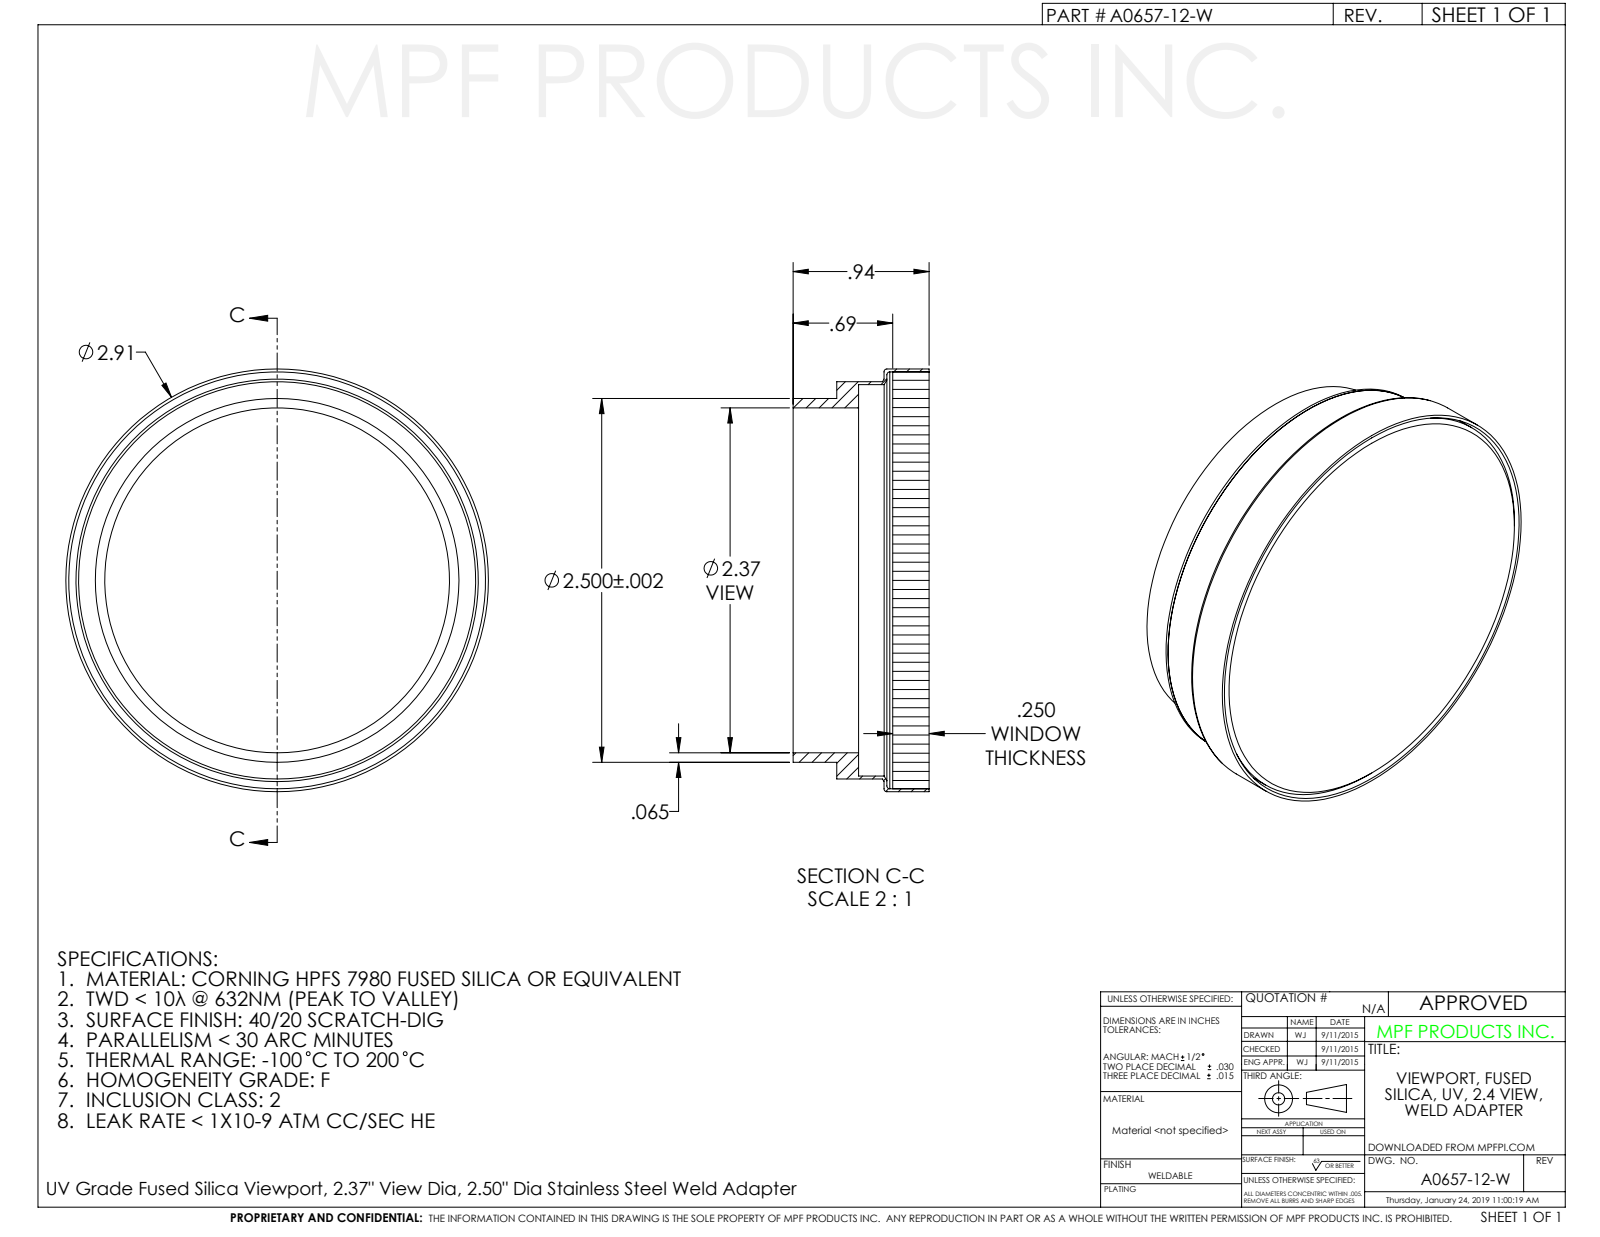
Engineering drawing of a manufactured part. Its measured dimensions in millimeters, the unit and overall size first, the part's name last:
Units: millimetres
Overall size (bounding box): 73.5 × 73.5 × 29.3
Round holes (diameter × count): ⌀60.2 ×1, ⌀72.8 ×1
Round bosses / shafts (diameter × count): ⌀73.5 ×1, ⌀63.5 ×1, ⌀62.2 ×1, ⌀61.6 ×1
Main face-to-face distances: 6.4, 21.1, 27.5, 13.8, 7.3, 13.6, 7.9, 5.9, 13.2, 19.6
Volume: 31 640 mm³ · Surface area: 23 110 mm²
Bodies: 1 solid, 28 faces (6 planar, 14 cylindrical, 8 other)
Part name (STEP PRODUCT): A0657-12-W
STEP written by: SolidWorks 2012 (CONFIG_CONTROL_DESIGN)
